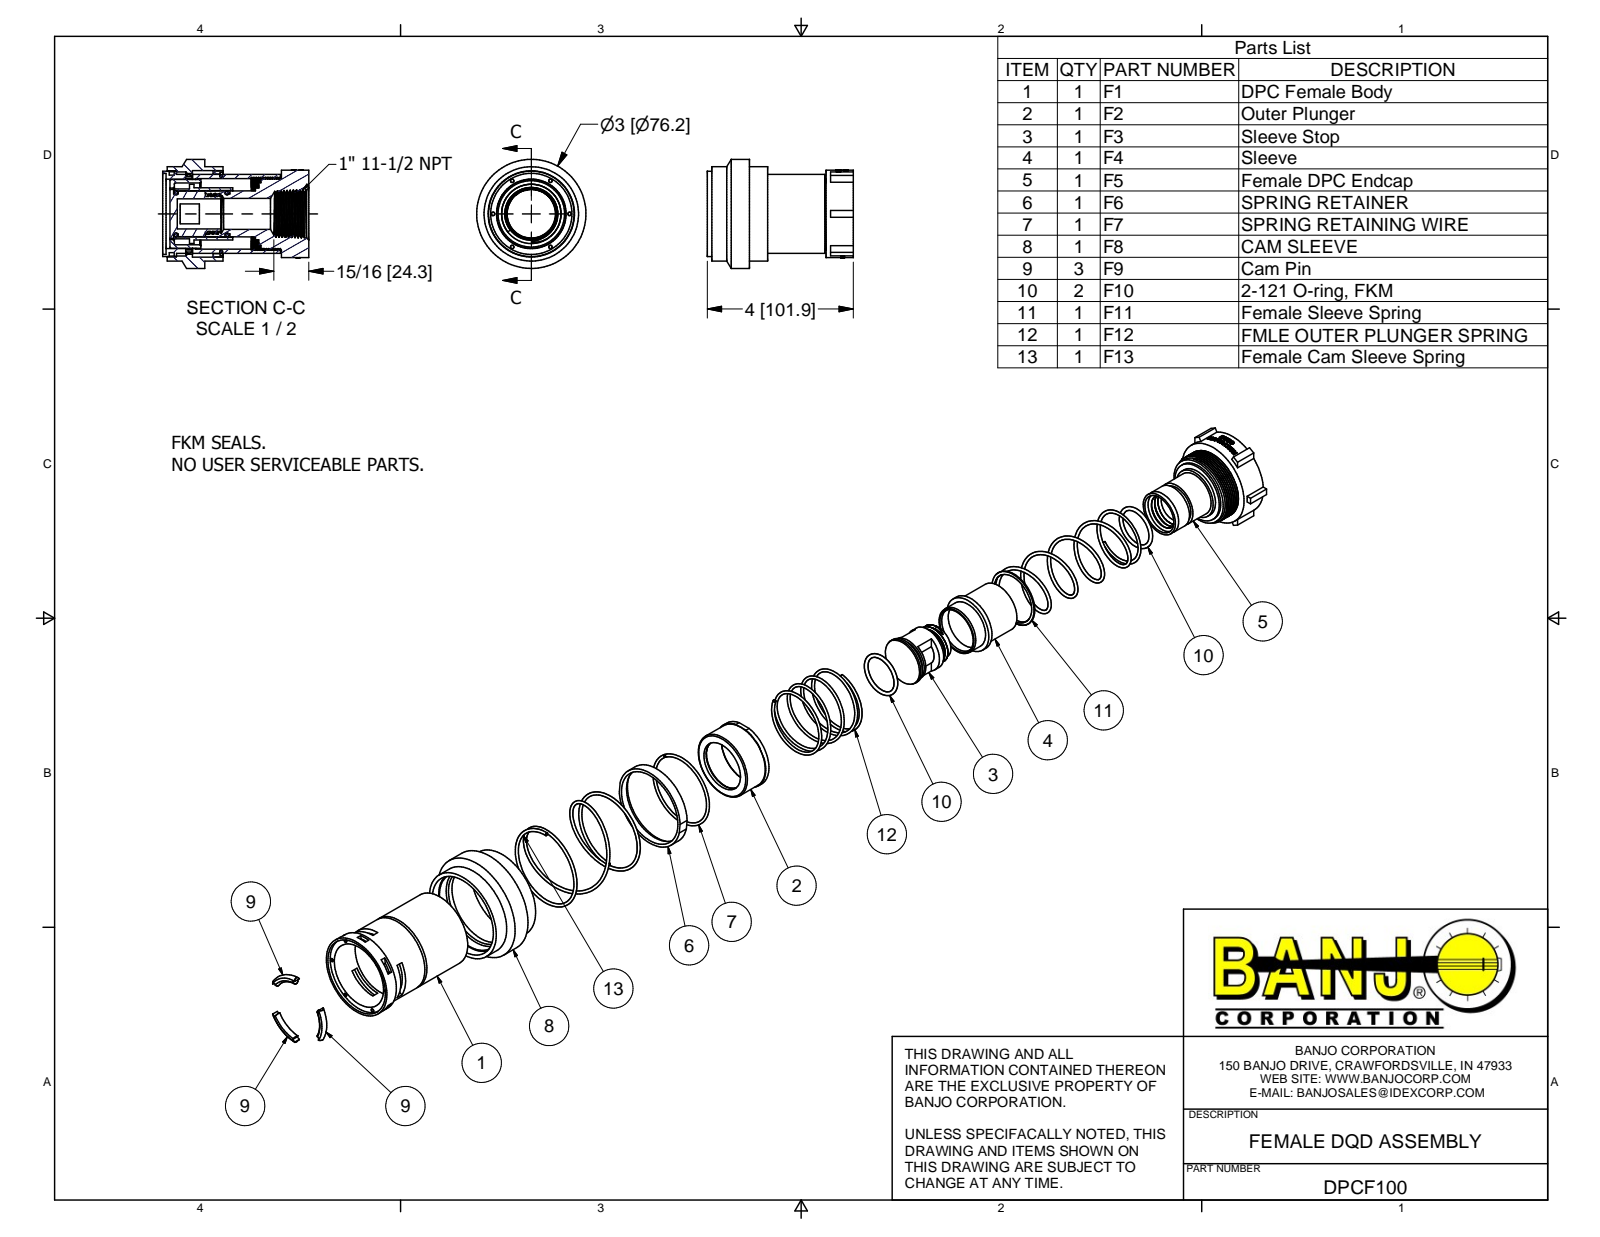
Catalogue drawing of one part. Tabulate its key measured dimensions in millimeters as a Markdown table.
| quantity | value |
| --- | --- |
| part name | F1; F2; F3; F4 (+7 more) |
| STEP written by | Autodesk Inventor 2016 (AUTOMOTIVE_DESIGN) |
| units | millimeters |
| bodies | 13 solids, 715 faces (321 planar, 132 cylindrical, 262 other) |
| overall size | 101.85 × 76.2 × 76.2 |
| volume | 190 775 mm³ |
| surface area | 107 900 mm² |
| round holes (diameter × count) | 2.39 × 6, 21.08 × 1, 21.59 × 1, 28.57 × 1, 32.26 × 1, 36.07 × 1, 43.18 × 1, 49.28 × 1, 49.28 × 1, 50.93 × 1, 55.58 × 1, 56.46 × 1 |
| round bosses / shafts (diameter × count) | 76.2 × 1, 65.88 × 1, 61.09 × 1, 59.94 × 1, 55.12 × 1, 50.76 × 1, 49.02 × 1, 48.51 × 1 |
| partial cylindrical surfaces (radius × count) | 7.75 × 1, 12.57 × 1, 13.25 × 1, 14.41 × 1, 16.38 × 1, 18.41 × 1, 27.05 × 1, 30.8 × 1 |
| main face-to-face distances | 96.82, 19.05, 24.34, 72.48, 77.77, 53.43, 2.54, 37.04, 12.7, 40.73 |
| hole center spacings | 26.67, 26.68, 46.19, 53.34, 26.66, 46.2 |
